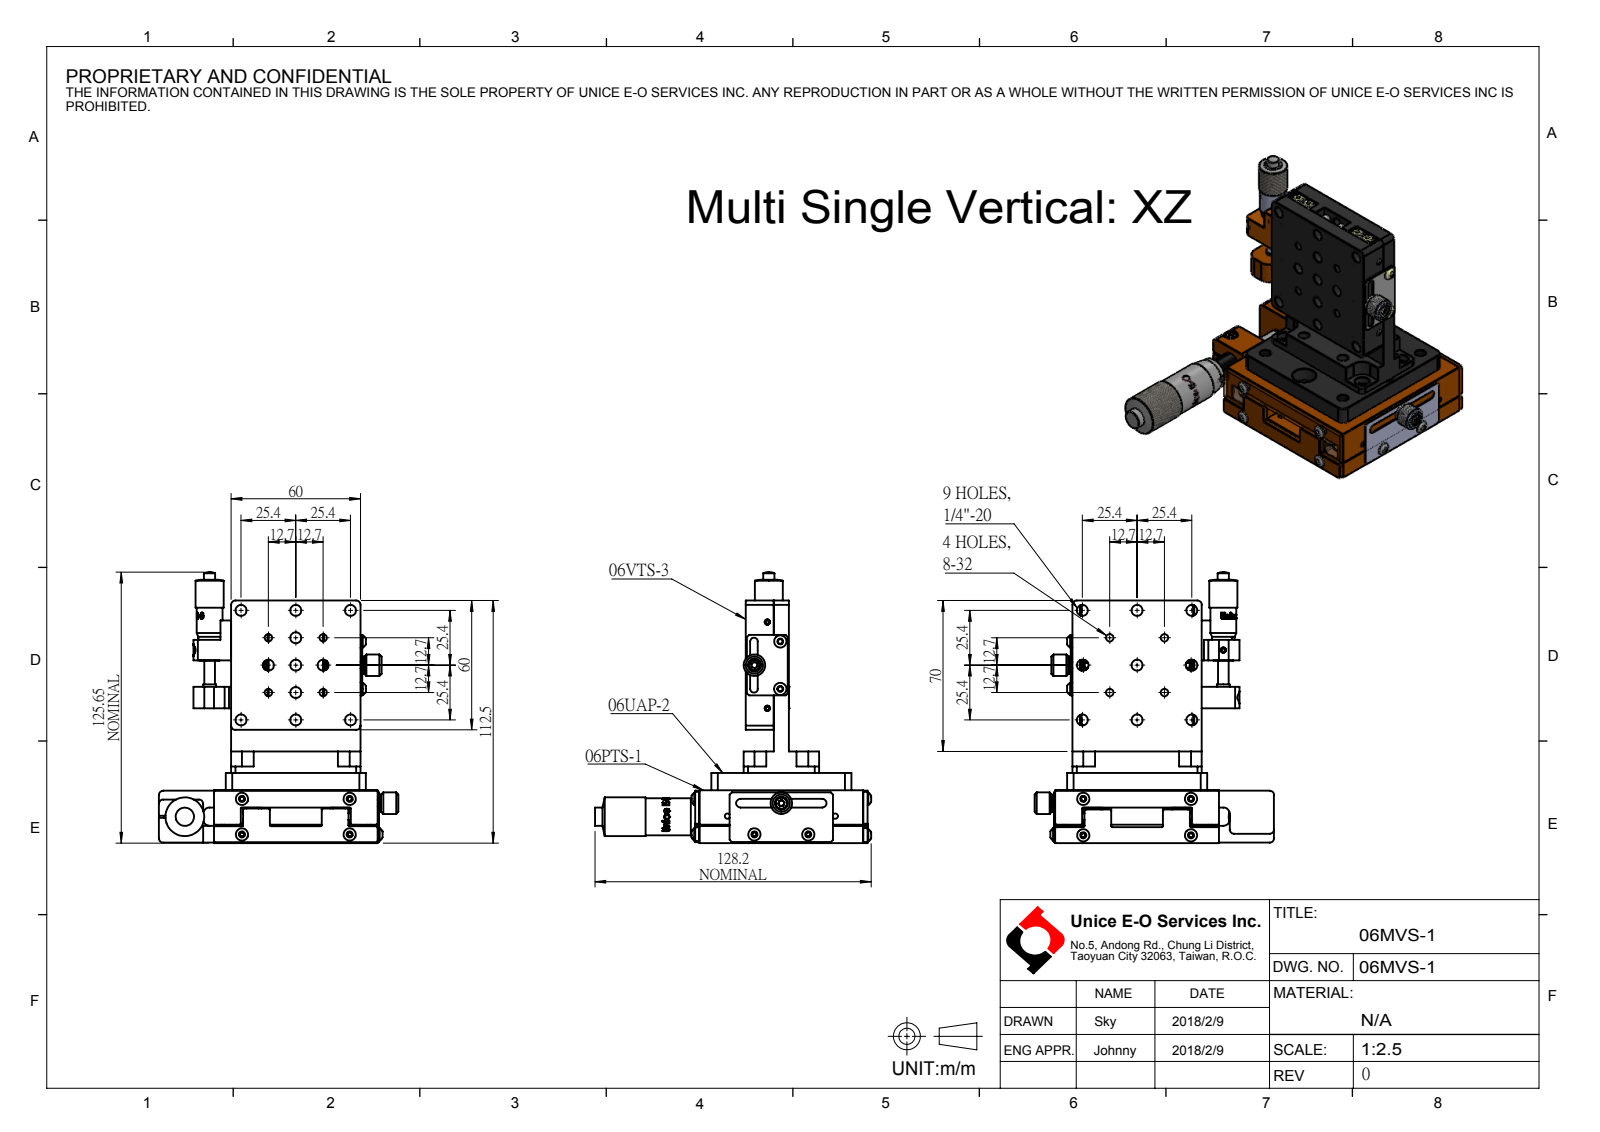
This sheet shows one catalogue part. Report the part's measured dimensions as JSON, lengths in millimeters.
{"part_name": "06MVS-1", "step_written_by": "SolidWorks 2016 (AUTOMOTIVE_DESIGN)", "units": "millimeters", "bodies": {"solids": 0, "faces": 1010, "planar": 474, "cylindrical": 391, "other": 145}, "overall_size": [128.15, 125.65, 111.1], "round_holes": [[2.5, 28], [5.11, 21], [3.45, 8], [6.5, 7], [5, 4], [7, 4], [11.11, 4], [6.7, 3], [6, 2], [9.5, 1], [10, 1]], "round_bosses_or_shafts": [[5.7, 10], [5, 5], [6, 3], [10, 2], [8, 2], [4.5, 2], [2.5, 2], [18, 1]], "partial_cylinders_radius": [[0.5, 31], [2, 20], [3, 6], [5, 4], [5.5, 4], [2.5, 3], [1.75, 2], [2.55, 2]], "face_to_face_distances": [8, 41.5, 16, 34.5, 20, 24.5, 16.5, 7, 76, 13], "hole_center_spacings": [17.96, 28.4, 25.4, 40.16, 12.7, 10, 20, 35.92]}
